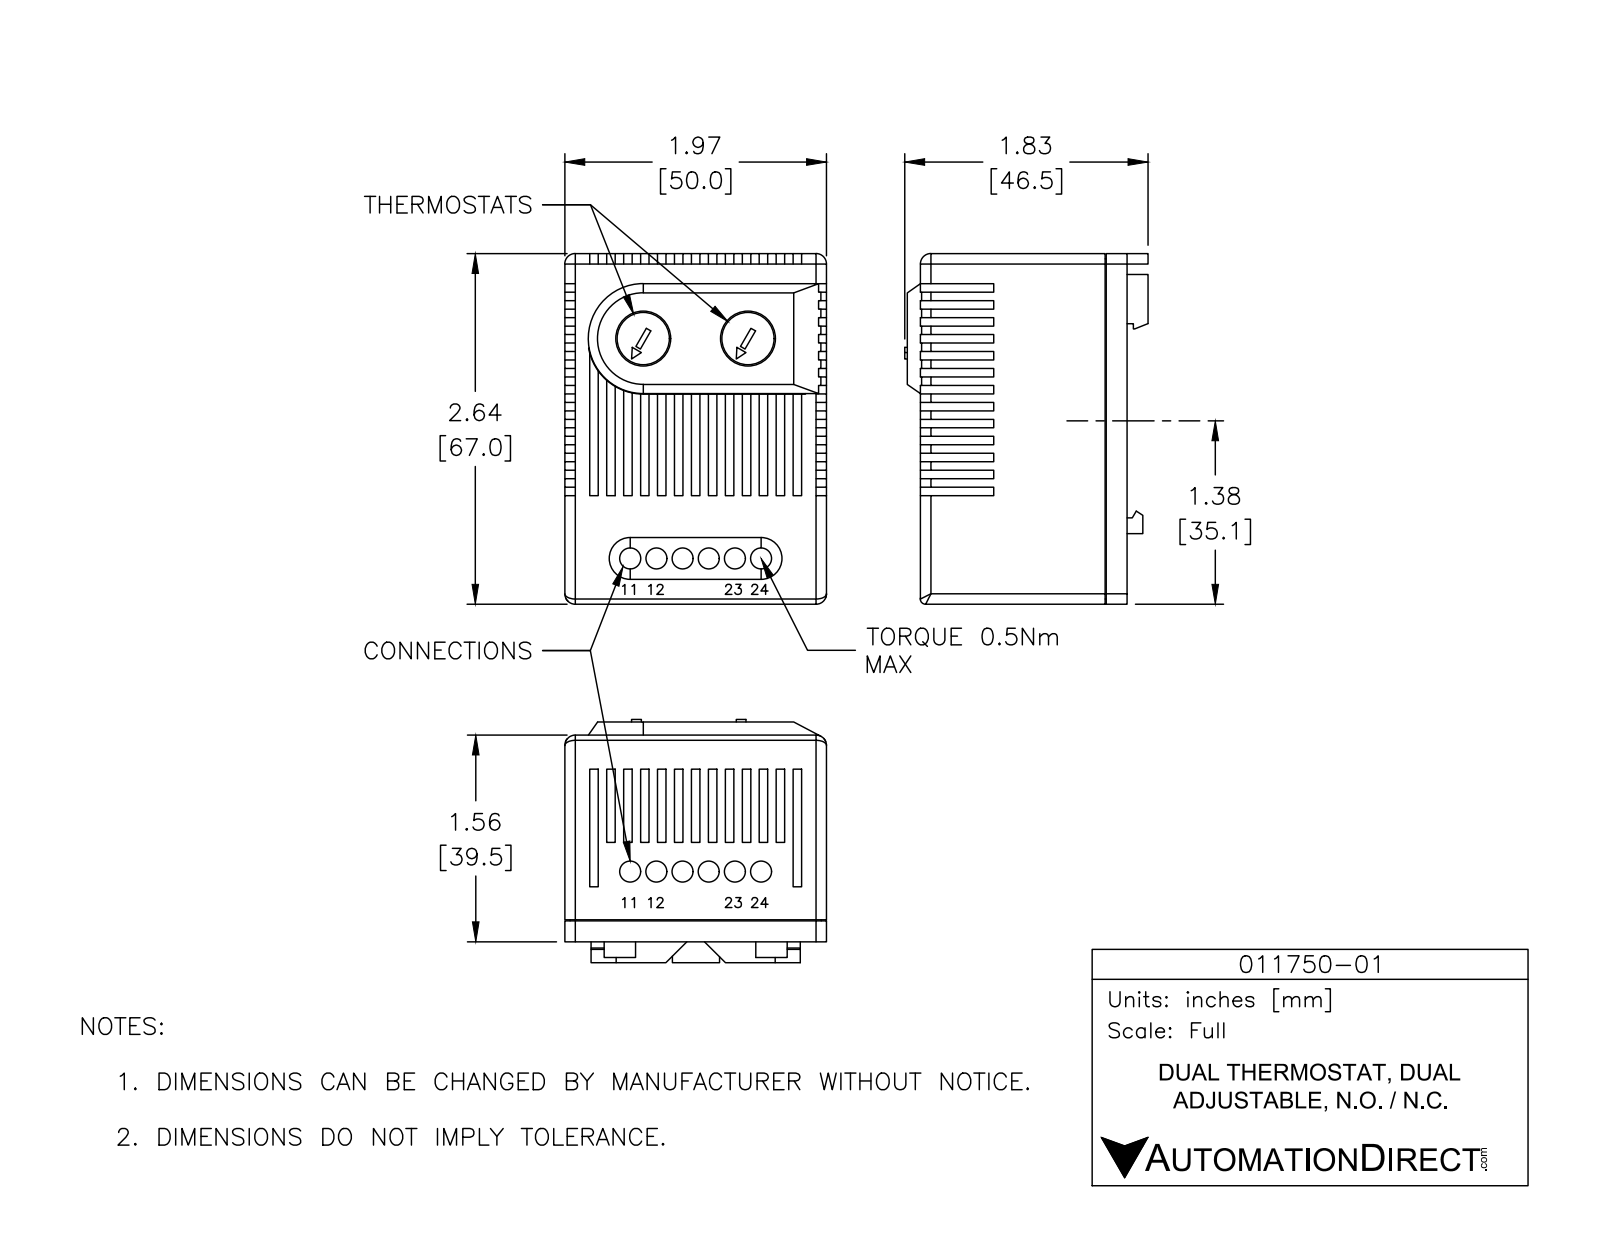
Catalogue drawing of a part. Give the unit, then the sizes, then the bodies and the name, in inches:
Units: inches
Overall size (bounding box): 2.656 × 1.969 × 1.831
Round holes (diameter × count): ⌀0.157 ×12, ⌀0.413 ×2
Round bosses / shafts (diameter × count): ⌀0.394 ×2
Partial cylindrical surfaces — rounded edges, fillets, slot ends (radius × count): R0.079 ×7, R0.039 ×5, R0.054 ×1, R0.06 ×1, R0.157 ×1, R0.413 ×1, R0.417 ×1
Main face-to-face distances: 1.969, 0.079, 0.128, 1.555, 2.638, 0.064, 0.255, 0.383, 0.191, 0.319
Hole centre spacings: 0.197, 0.394, 0.591, 0.787, 1.656, 0.984, 1.68, 1.725
Volume: 7.939 in³ · Surface area: 35.94 in²
Bodies: 2 solids, 656 faces (507 planar, 93 cylindrical, 56 other)
Part name (STEP PRODUCT): 011750-01
STEP written by: SolidWorks 2017 (AUTOMOTIVE_DESIGN)
